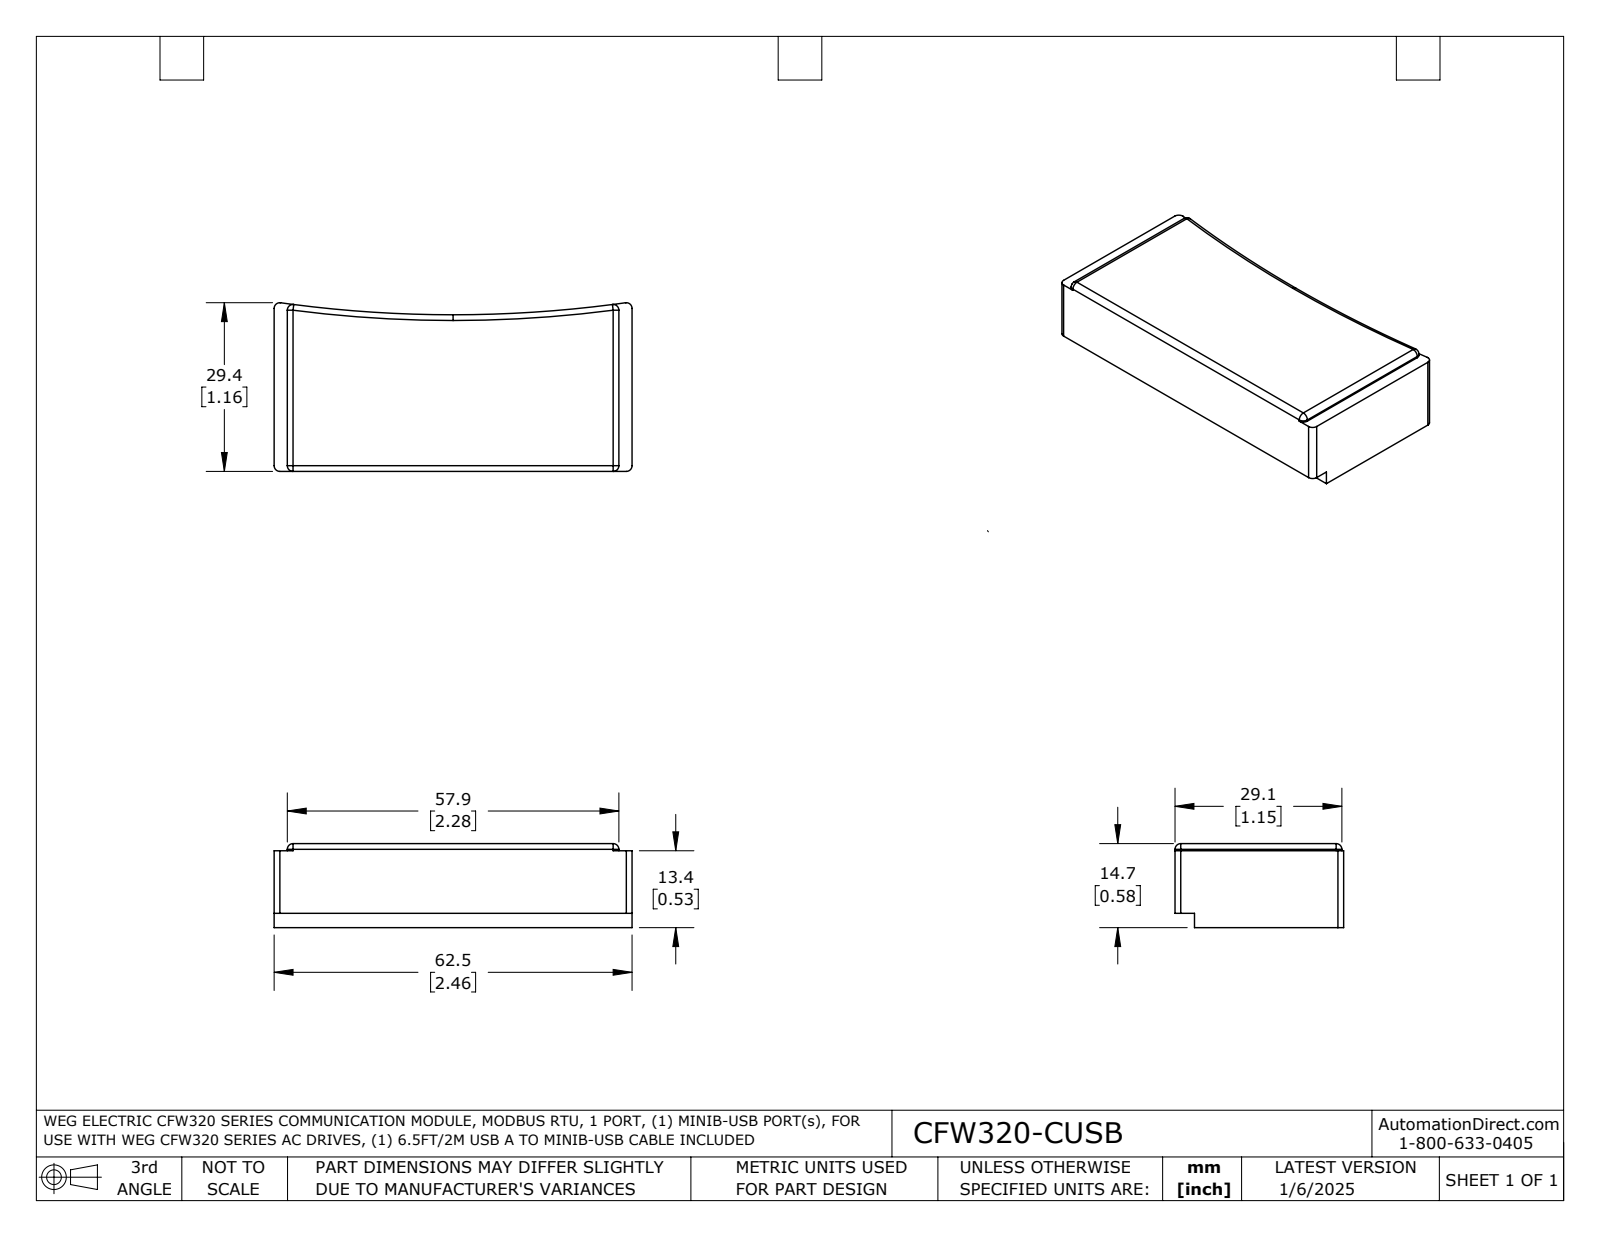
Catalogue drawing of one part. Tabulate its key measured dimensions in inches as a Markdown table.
| quantity | value |
| --- | --- |
| part name | CFW320-CUSB |
| STEP written by | SolidWorks 2021 (AUTOMOTIVE_DESIGN) |
| units | inches |
| bodies | 1 solid, 33 faces (11 planar, 16 cylindrical, 6 other) |
| overall size | 2.461 × 1.159 × 0.578 |
| volume | 1.526 in³ |
| surface area | 9.429 in² |
| partial cylindrical surfaces (radius × count) | 0.039 × 11, 8.543 × 1 |
| main face-to-face distances | 0.577, 2.461, 0.098, 0.479, 0.134, 0.528, 0.43, 0.049, 0.091, 2.37 |
